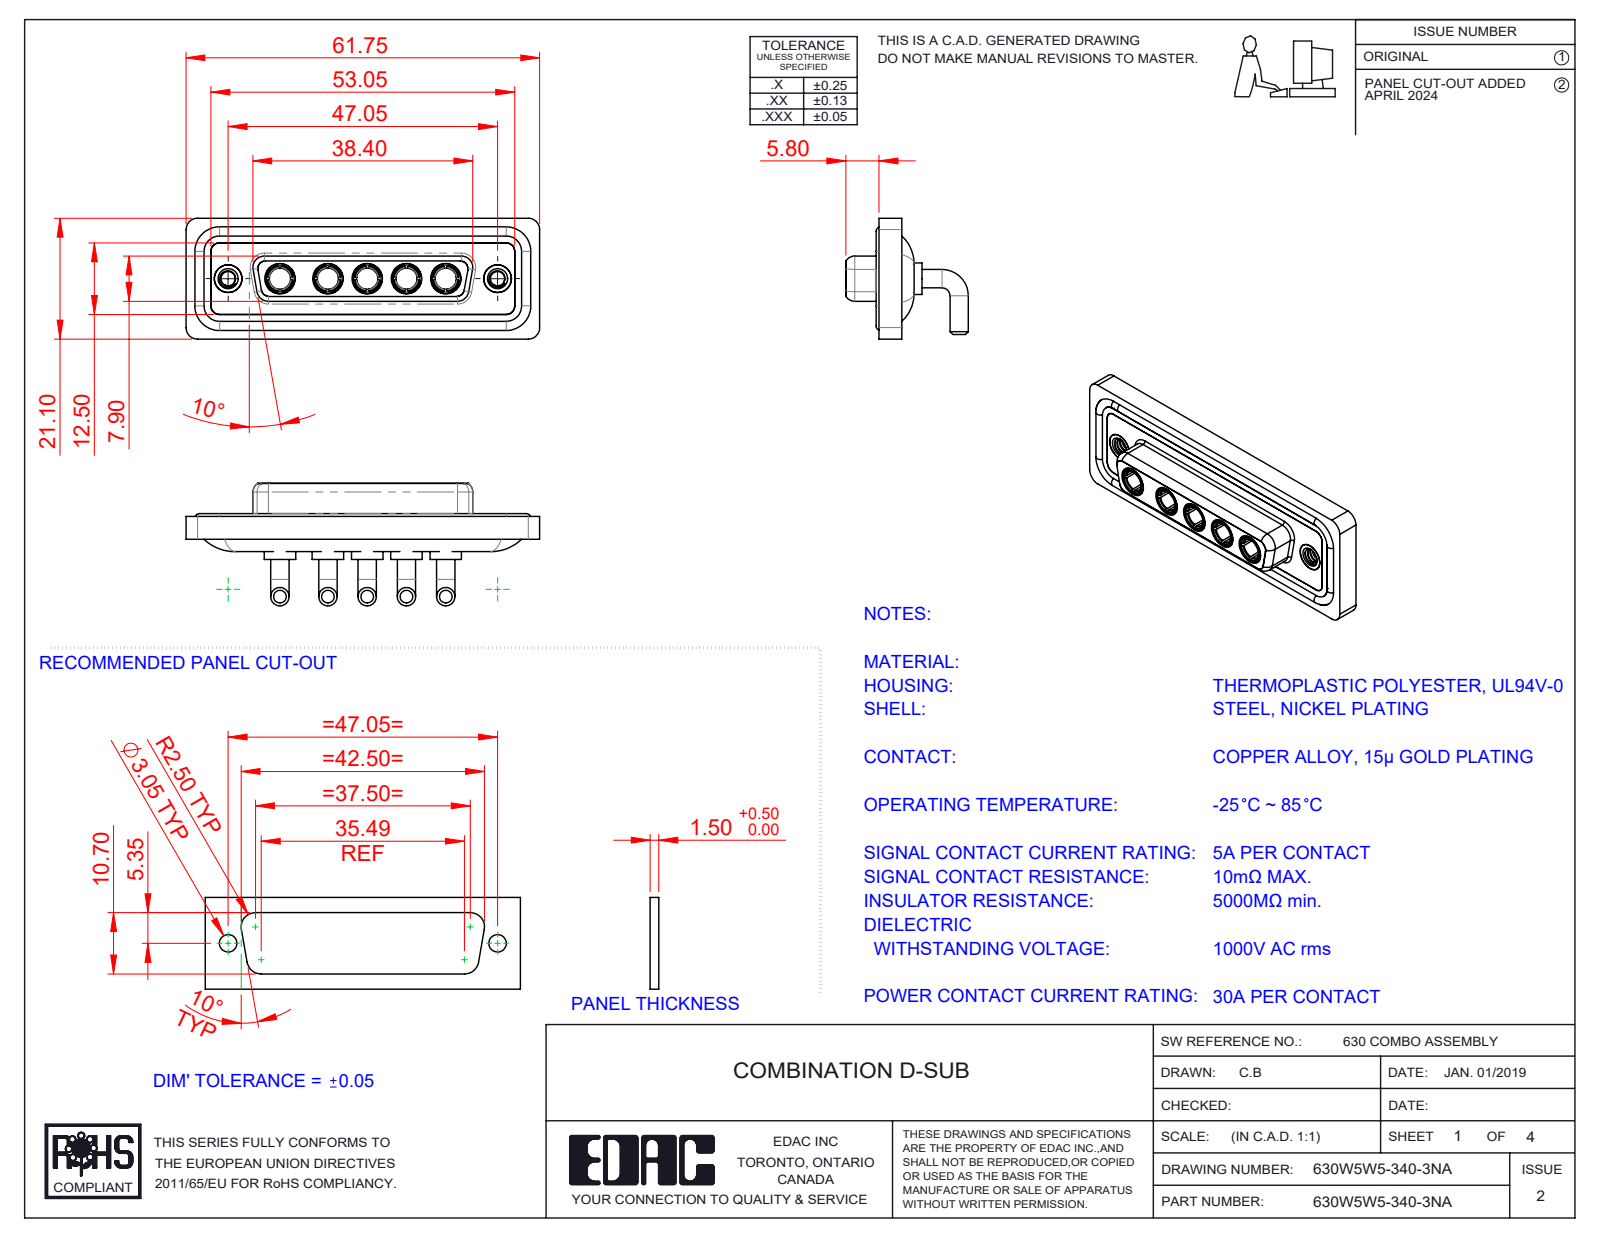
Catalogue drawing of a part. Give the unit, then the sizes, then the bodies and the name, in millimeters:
Units: millimetres
Overall size (bounding box): 61.75 × 21.4 × 21.1
Round holes (diameter × count): ⌀4.85 ×7, ⌀3.7 ×5, ⌀5.3 ×5, ⌀2.5 ×2, ⌀4 ×2, ⌀4.05 ×2, ⌀5 ×2
Round bosses / shafts (diameter × count): ⌀3.2 ×10, ⌀5.5 ×5, ⌀5.2 ×5, ⌀4.96 ×5, ⌀4.75 ×5, ⌀3.75 ×5, ⌀1.6 ×4, ⌀4.95 ×2
Partial cylindrical surfaces — rounded edges, fillets, slot ends (radius × count): R1.5 ×18, R2 ×18, R1.35 ×8, R1.6 ×8, R2.1 ×5, R0.25 ×4, R0.5 ×4, R0.6 ×4
Main face-to-face distances: 0.4, 1.8, 4.1, 1.1, 1.5, 2.5, 3.1, 3.7, 1.6, 2.9
Hole centre spacings: 6.86, 9.04, 38.01, 6.87, 8.38, 13.72, 13.73, 15.25
Volume: 8 568 mm³ · Surface area: 13 908 mm²
Bodies: 17 solids, 770 faces (250 planar, 311 cylindrical, 209 other)
Part name (STEP PRODUCT): 630Combo Housing_5W5; 630W5W5-340-3NA; 630Combo Shell Rear_25 Contacts; 630Combo Waterproof Housing_25 Contacts (+3 more)
STEP written by: SolidWorks 2023 (CONFIG_CONTROL_DESIGN)
